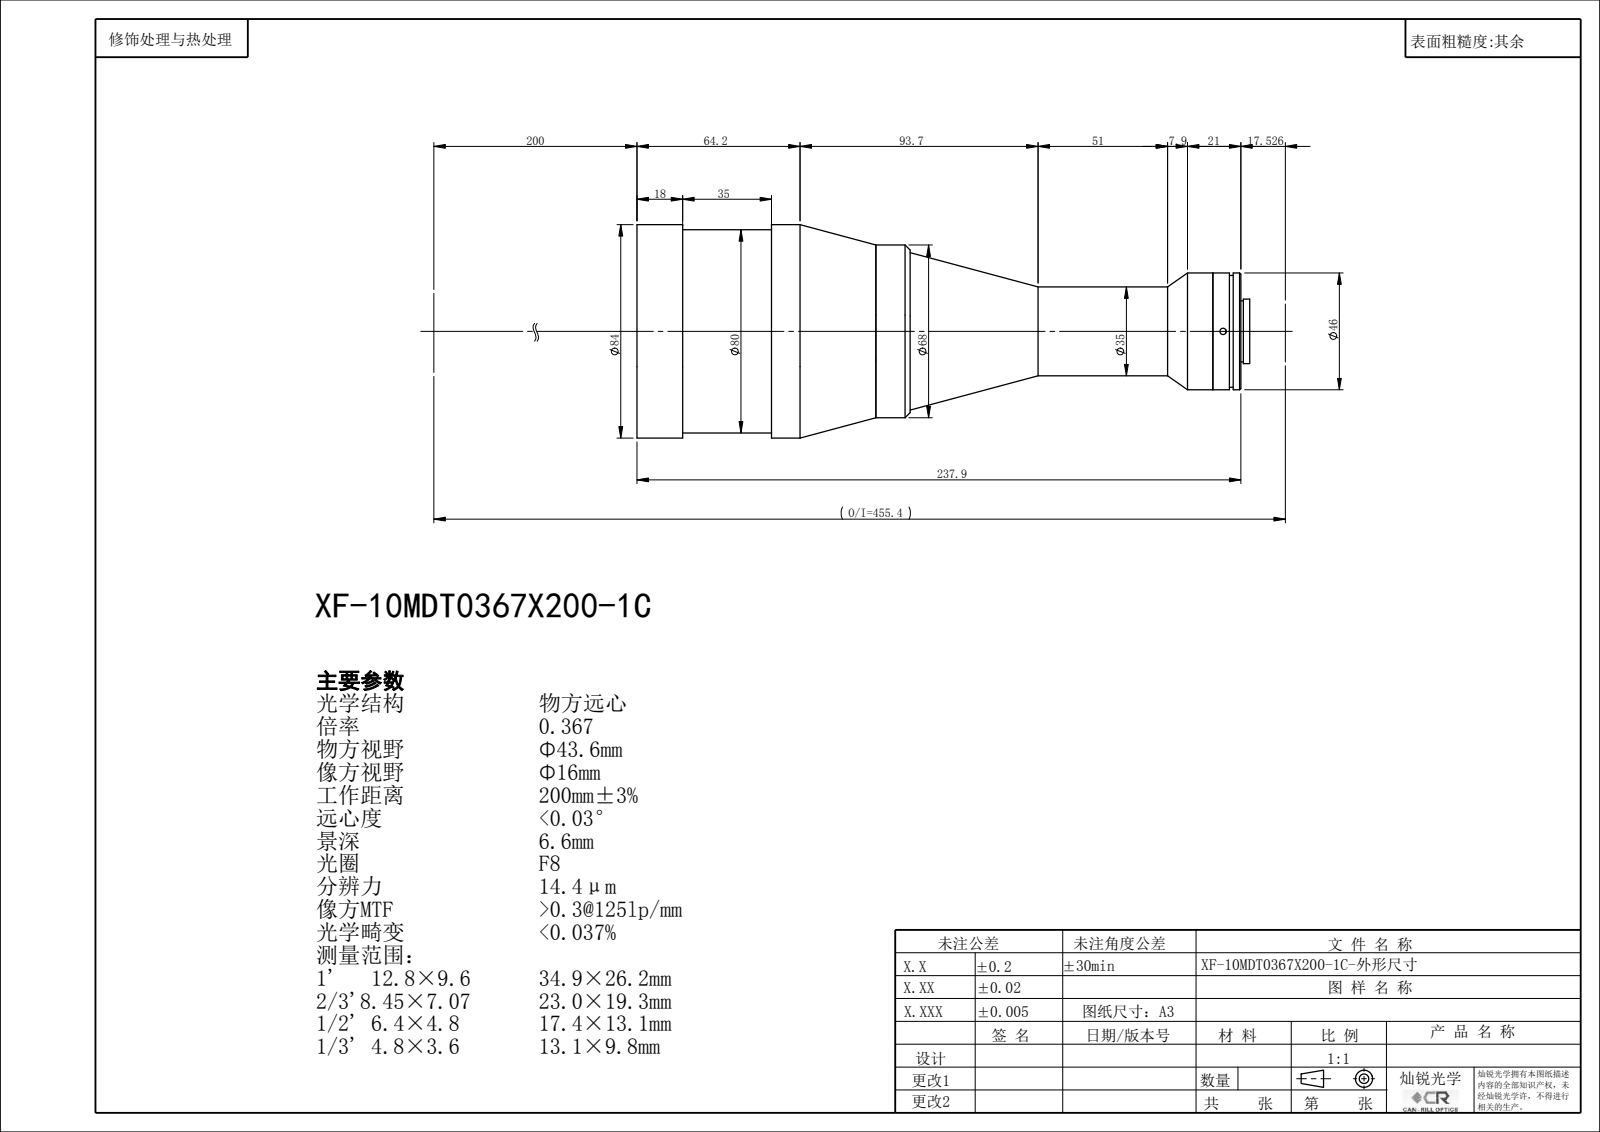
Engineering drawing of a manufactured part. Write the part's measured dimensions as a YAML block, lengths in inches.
part_name: "XF-5MDT0367X200-1C"
step_written_by: "SolidWorks 2014 (CONFIG_CONTROL_DESIGN)"
units: inches
bodies: {solids: 0, faces: 83, planar: 27, cylindrical: 42, other: 14}
overall_size: [9.502, 3.307, 3.307]
round_holes:
  - {diameter: 0.098, count: 3}
  - {diameter: 0.807, count: 1}
  - {diameter: 1.142, count: 1}
  - {diameter: 2.441, count: 1}
  - {diameter: 2.717, count: 1}
  - {diameter: 3.031, count: 1}
round_bosses_or_shafts:
  - {diameter: 3.307, count: 1}
  - {diameter: 3.15, count: 1}
  - {diameter: 2.677, count: 1}
  - {diameter: 1.811, count: 1}
  - {diameter: 1.732, count: 1}
  - {diameter: 1.575, count: 1}
  - {diameter: 1.378, count: 1}
  - {diameter: 1, count: 1}
face_to_face_distances: [5.66, 3.705, 9.365, 0.198, 3.507, 9.167, 0.709, 0.511, 2.996, 8.656]
